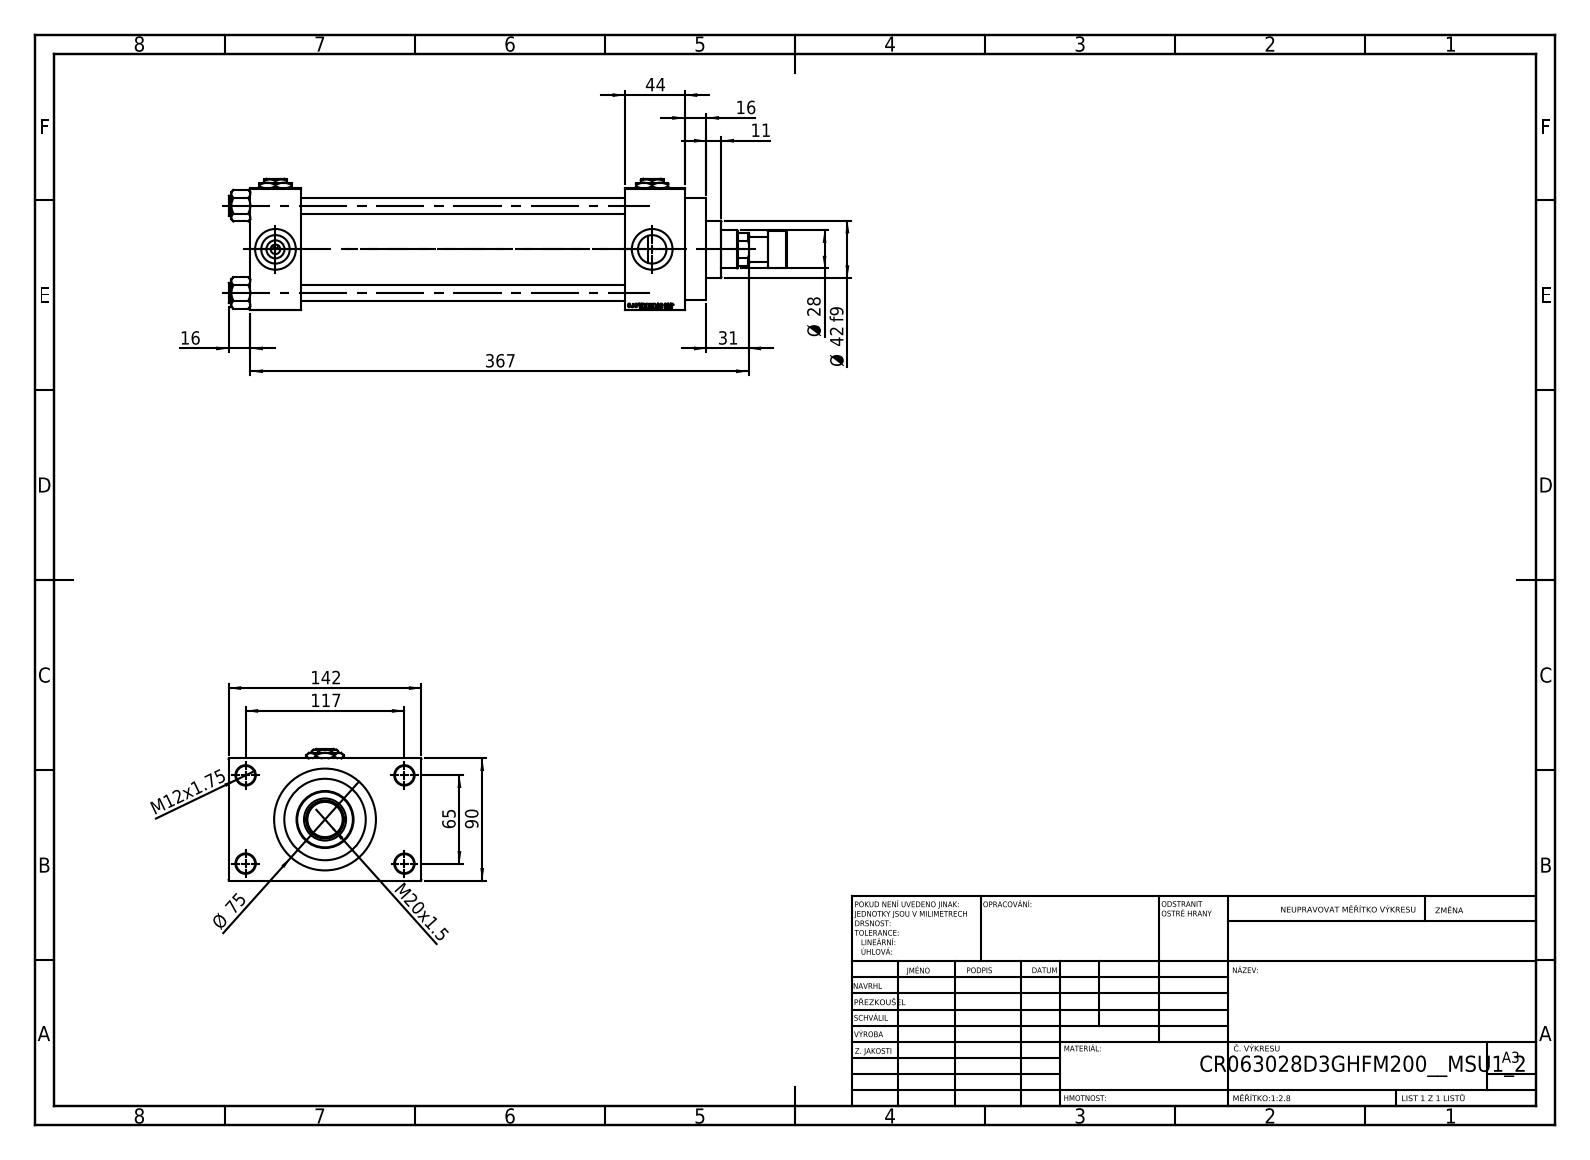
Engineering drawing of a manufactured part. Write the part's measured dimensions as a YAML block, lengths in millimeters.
part_name: "NUT_M5_D; V215_VC_A; V215CR_D_TYCINKA; V215CR_ROD_END_F (+3 more)"
step_written_by: "SolidWorks 2019 (CONFIG_CONTROL_DESIGN)"
units: millimeters
bodies: {solids: 14, faces: 1218, planar: 549, cylindrical: 103, other: 566}
overall_size: [411, 142, 97]
volume: 1407000
surface_area: 325819
round_holes:
  - {diameter: 12, count: 4}
  - {diameter: 14, count: 4}
  - {diameter: 20.96, count: 4}
  - {diameter: 30, count: 4}
  - {diameter: 7, count: 3}
  - {diameter: 18.5, count: 1}
  - {diameter: 28, count: 1}
  - {diameter: 31, count: 1}
  - {diameter: 50, count: 1}
  - {diameter: 60, count: 1}
  - {diameter: 63, count: 1}
round_bosses_or_shafts:
  - {diameter: 15, count: 4}
  - {diameter: 75, count: 1}
  - {diameter: 69, count: 1}
  - {diameter: 42, count: 1}
  - {diameter: 27, count: 1}
  - {diameter: 18, count: 1}
face_to_face_distances: [90, 239, 37, 276, 283, 320, 44, 26, 116, 16]
hole_center_spacings: [26.35, 45.47, 64.3, 66.92, 69.81, 90.65, 111.34, 65]
